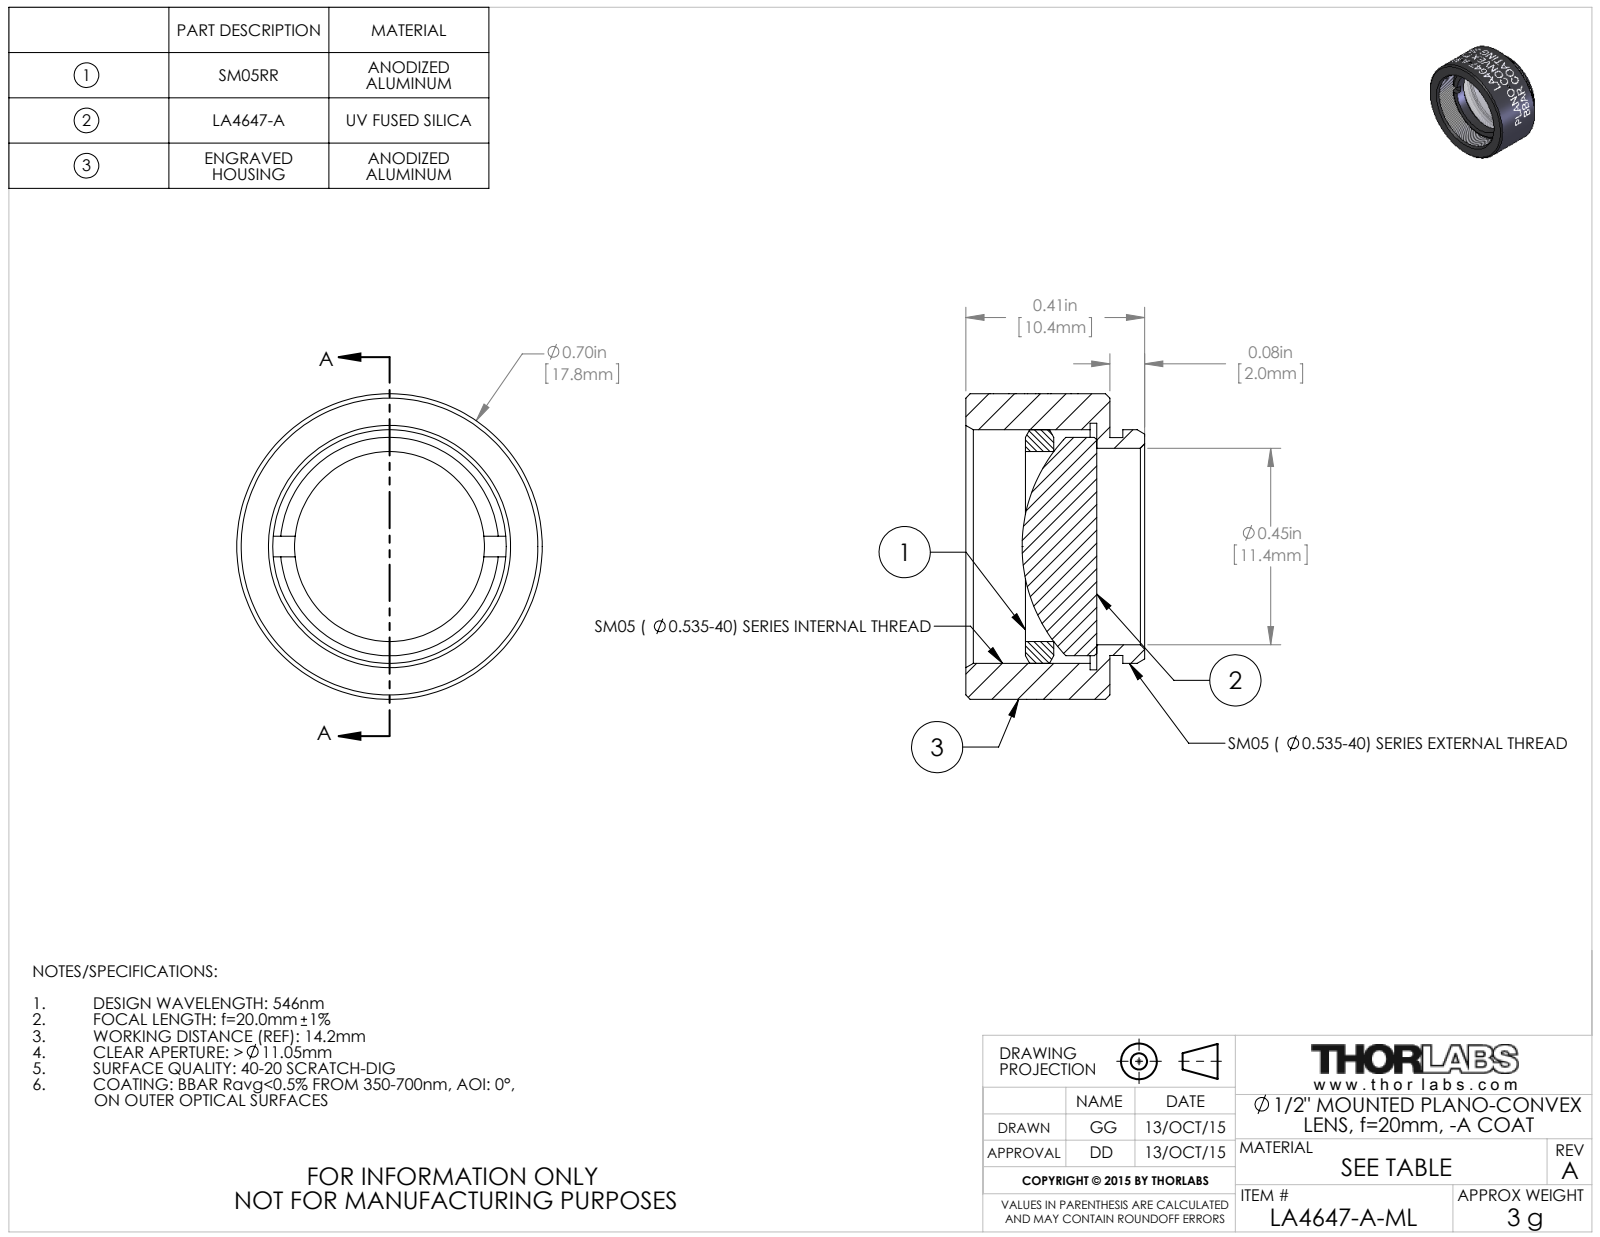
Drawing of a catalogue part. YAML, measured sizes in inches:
part_name: "TTN039333-E0W"
step_written_by: "SolidWorks 2014 (CONFIG_CONTROL_DESIGN)"
units: inches
bodies: {solids: 3, faces: 145, planar: 16, cylindrical: 108, other: 21}
overall_size: [0.7, 0.7, 0.41]
volume: 0.087
surface_area: 2.877
round_holes:
  - {diameter: 0.435, count: 1}
  - {diameter: 0.45, count: 1}
  - {diameter: 0.535, count: 1}
  - {diameter: 0.565, count: 1}
round_bosses_or_shafts:
  - {diameter: 0.7, count: 1}
  - {diameter: 0.535, count: 1}
  - {diameter: 0.5, count: 1}
  - {diameter: 0.499, count: 1}
face_to_face_distances: [0.03, 0.33, 0.3, 0.128, 0.098, 0.202, 0.193, 0.163, 0.065, 0.137]
